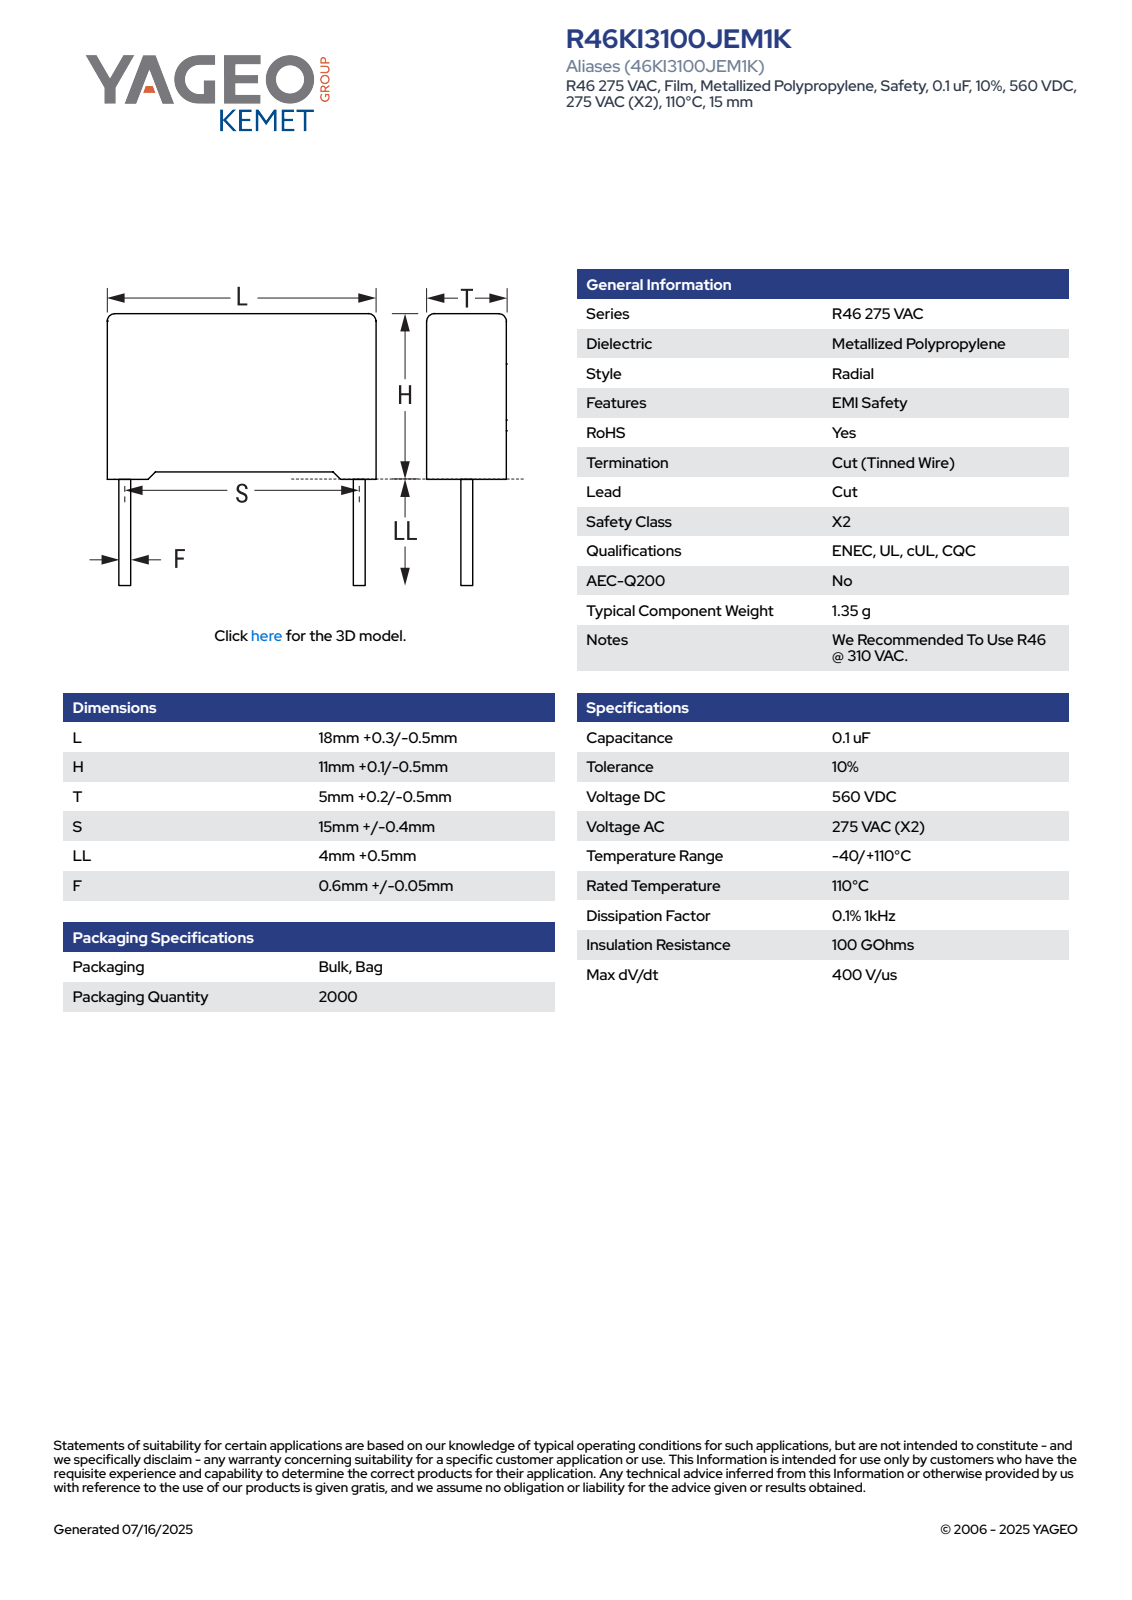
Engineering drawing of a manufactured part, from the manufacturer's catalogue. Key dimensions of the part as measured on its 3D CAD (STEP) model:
Part name (STEP PRODUCT): CFR_RB2_18X11X5_L18.3H11.1T5.2S15LL4.5F0.65
STEP written by: SolidWorks 2021 (AUTOMOTIVE_DESIGN)
Units: millimetres
Bodies: 4 solids, 85 faces (77 planar, 8 cylindrical, 0 other)
Overall size (bounding box): 18.3 × 15.6 × 5.21
Volume: 1 001 mm³ · Surface area: 763 mm²
Round bosses / shafts (diameter × count): ⌀0.65 ×2
Partial cylindrical surfaces — rounded edges, fillets, slot ends (radius × count): R0.5 ×4
Main face-to-face distances: 5.2, 10.35, 18.3, 0.61, 4.59, 0.37, 10.72, 0.38, 0.75, 11.1
